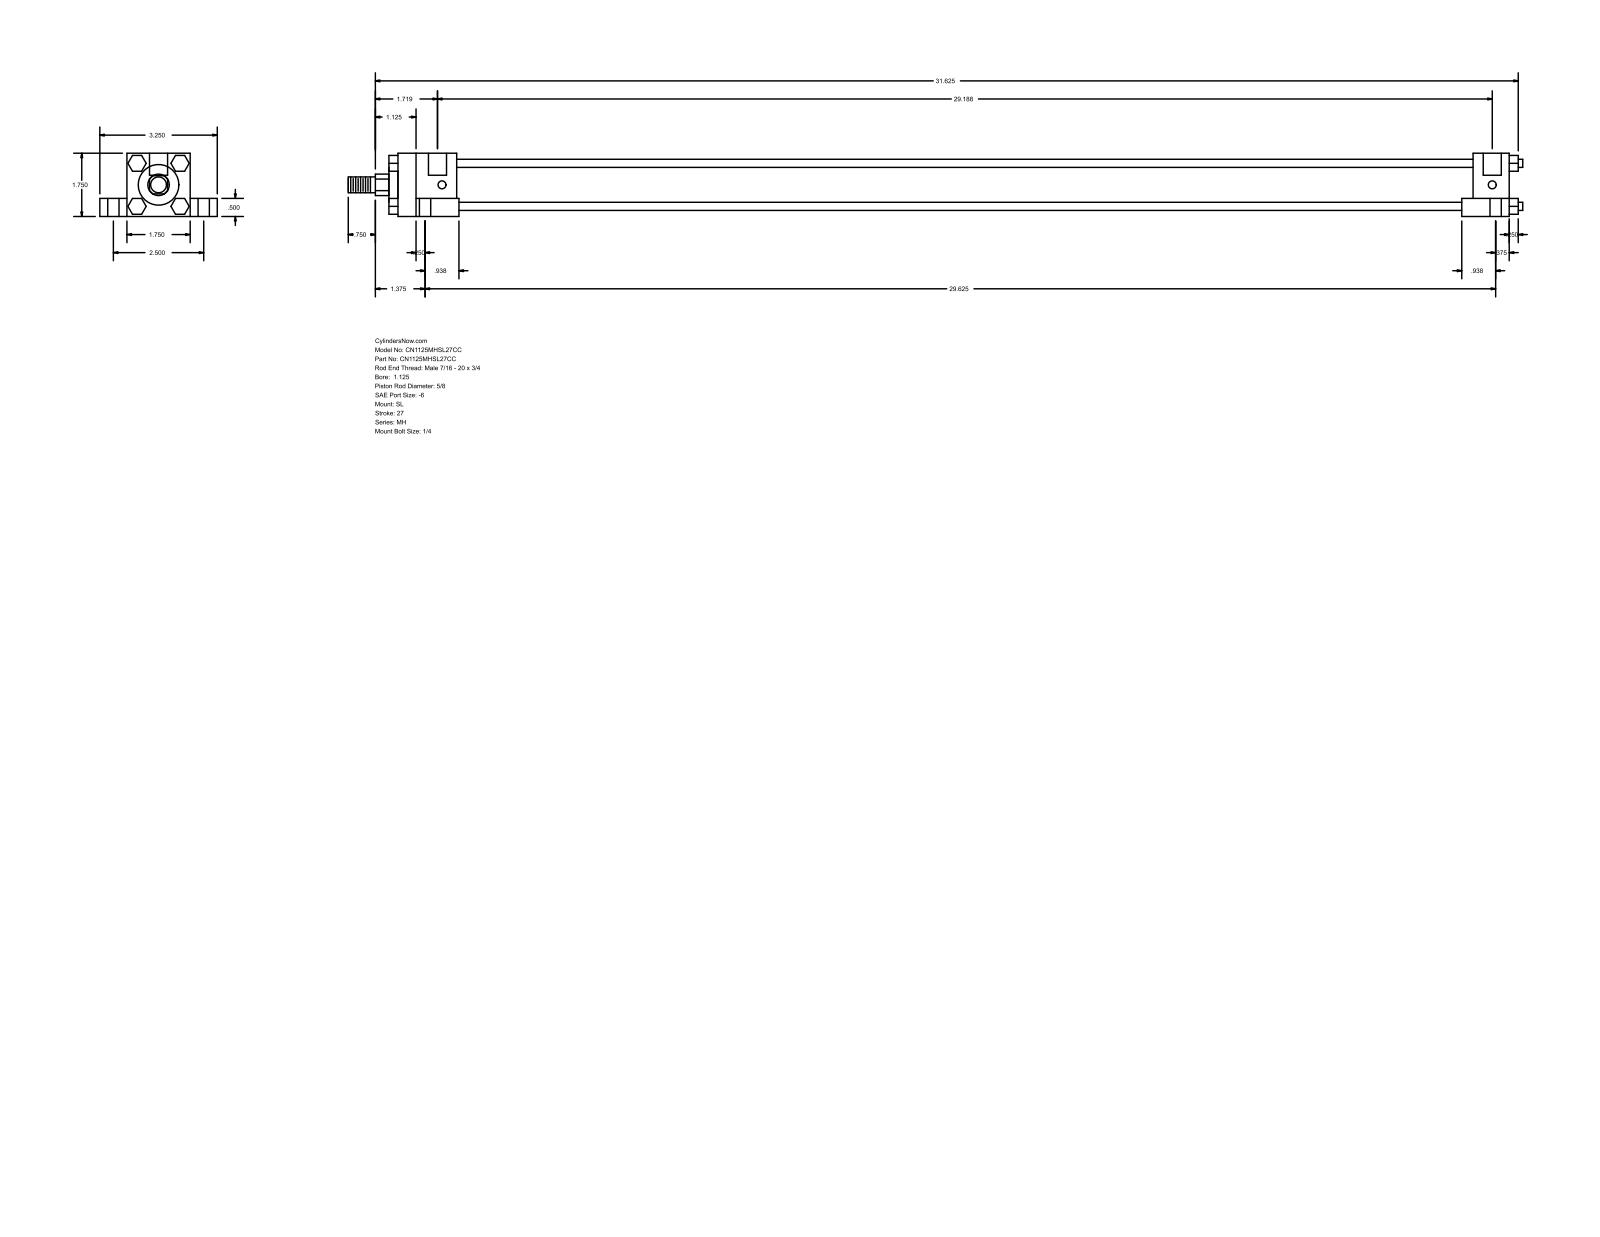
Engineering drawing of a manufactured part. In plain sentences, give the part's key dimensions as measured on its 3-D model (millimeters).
The part is named "MH_SL__0112_0.625". Its 3-D file was written by "GSSL Pune (CONFIG_CONTROL_DESIGN)". It is 0 solids with 150 faces: 114 planar, 36 cylindrical and 0 other. Overall it measures 825.5 by 82.55 by 44.45 millimeters. Round holes: 4 of diameter 5.56, 4 of diameter 7.94, 4 of diameter 14.29, 2 of diameter 12.7. Round bosses or shafts: 4 of diameter 5.71, 1 of diameter 34.92, 1 of diameter 28.57, 1 of diameter 15.88, 1 of diameter 11.11. Partial cylindrical surfaces (rounded edges, fillets, slot ends): 1 of radius 7.54. The main face-to-face distances are 44.46, 19.04, 12.7, 31.76, 63.5, 6.35, 787.39, 11.11, 47.62, 25.4. The hole center spacings are 31.84, 32.23, 32.93, 63.5, 738.19, 741.25, 744.42, 747.59.
